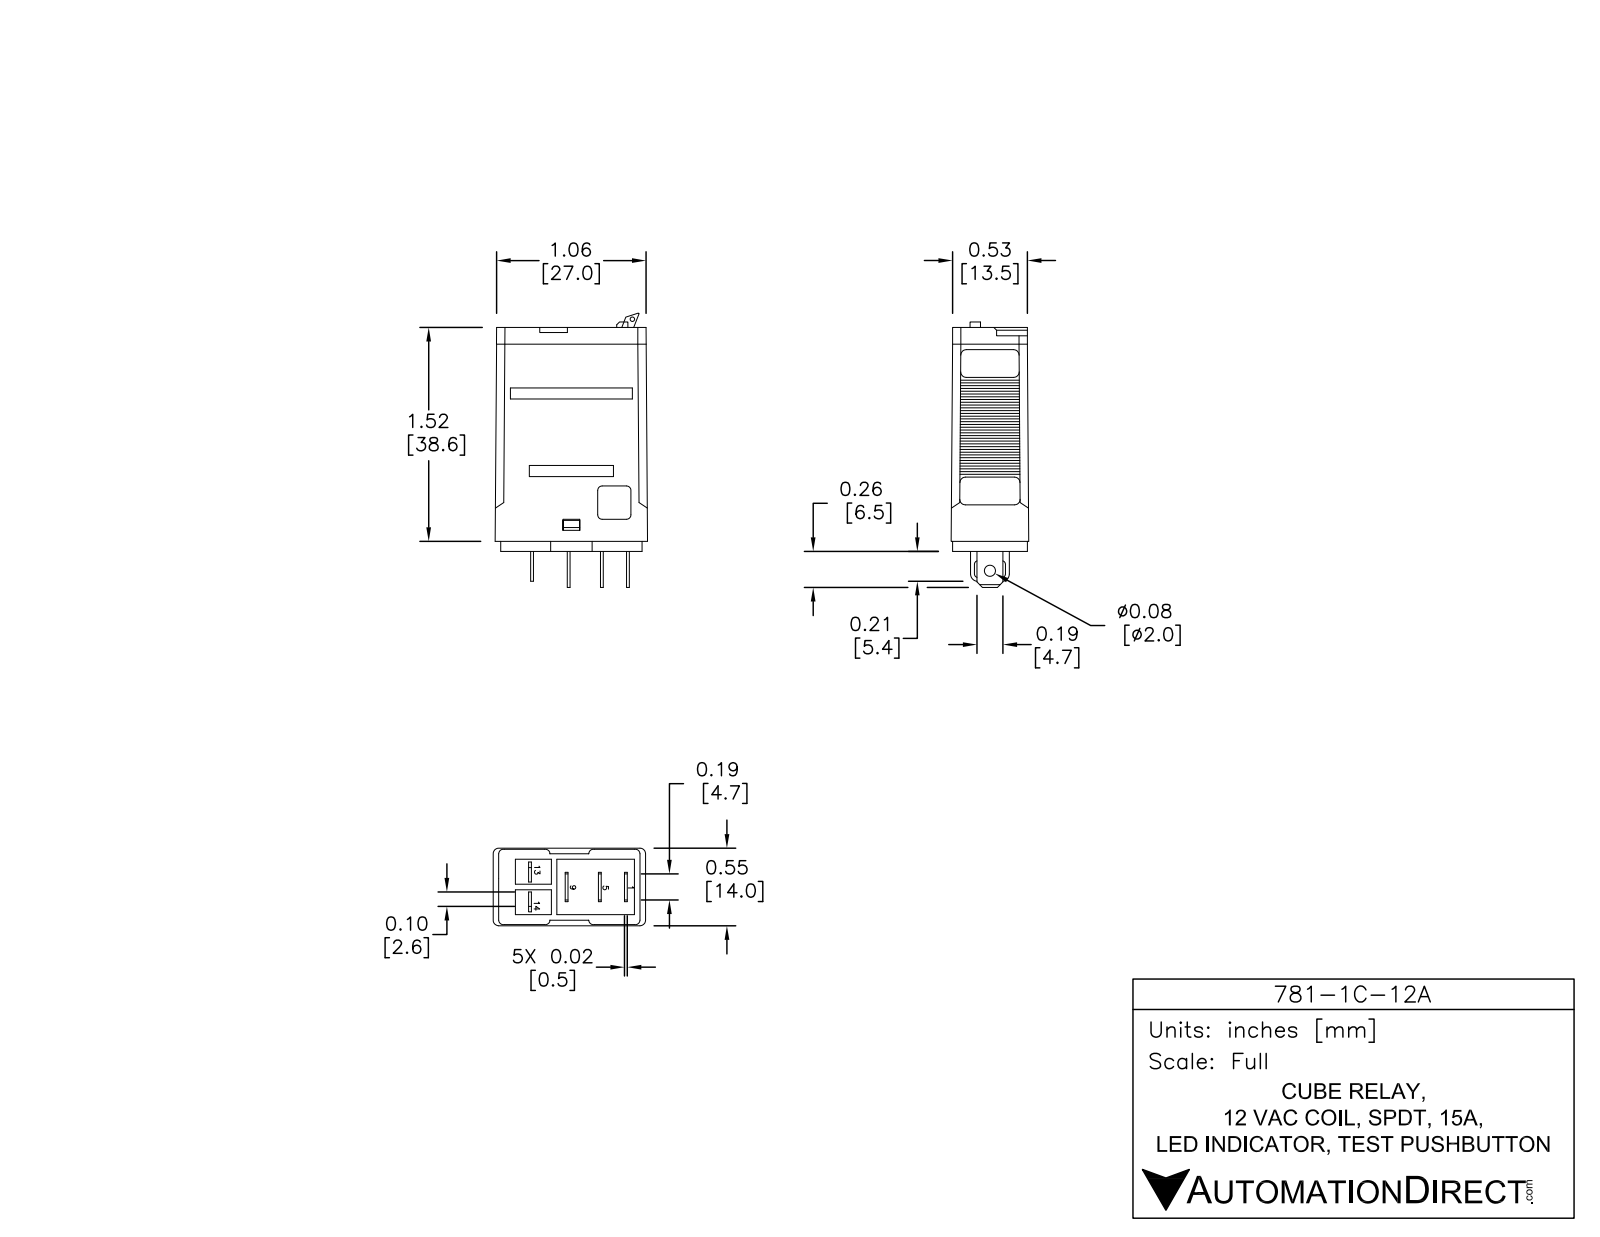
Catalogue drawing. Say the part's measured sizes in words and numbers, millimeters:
The part is named "781-1C-12A". Its 3-D file was written by "SolidWorks 2013 (AUTOMOTIVE_DESIGN)". It is 10 solids with 248 faces: 171 planar, 30 cylindrical and 47 other. Overall it measures 47.35 by 27.5 by 14.12 millimeters. Its volume is 15 229 cubic millimeters and its surface area 5 981 square millimeters. Round holes: 1 of diameter 1.85. Round bosses or shafts: 1 of diameter 0.83. Partial cylindrical surfaces (rounded edges, fillets, slot ends): 4 of radius 0.5, 4 of radius 0.56, 4 of radius 1.5, 2 of radius 1.32, 1 of radius 3.78. The main face-to-face distances are 14, 35.5, 27.5, 1.75, 37.25, 40.25, 38.5, 3, 2, 39.25.
